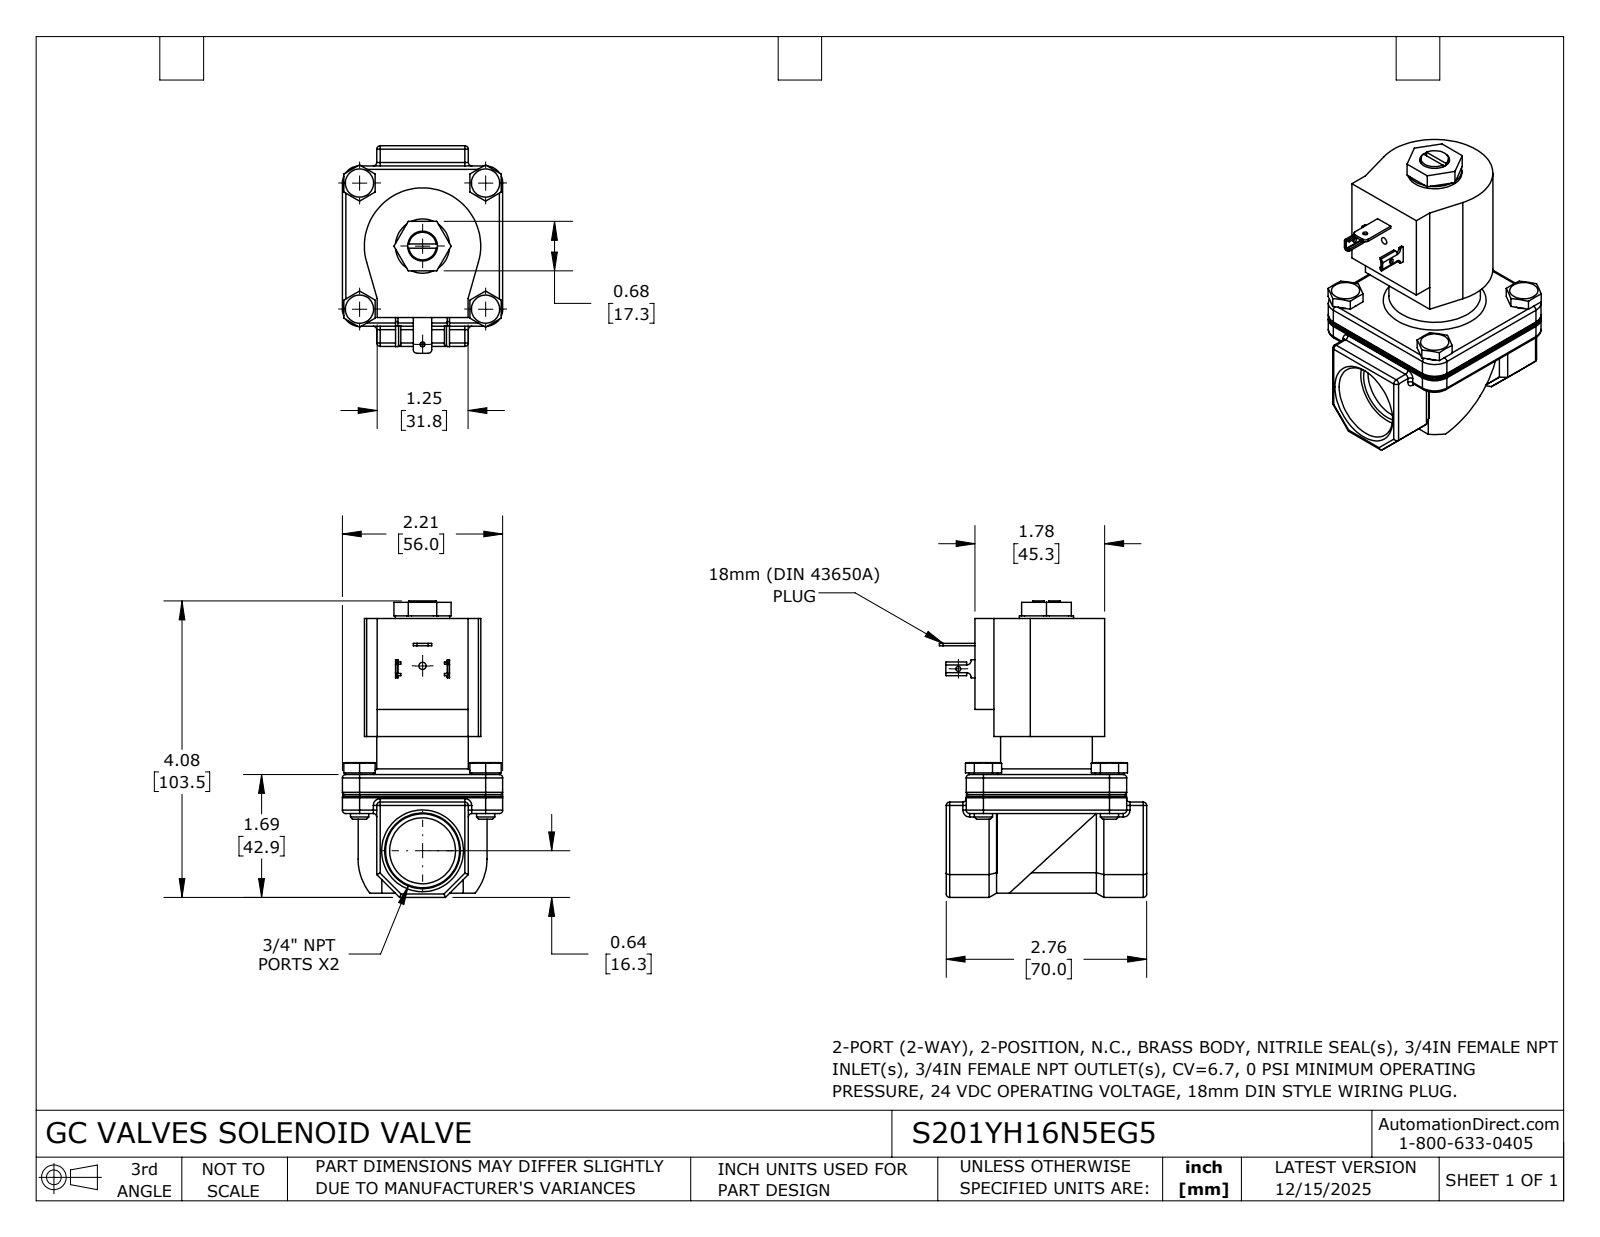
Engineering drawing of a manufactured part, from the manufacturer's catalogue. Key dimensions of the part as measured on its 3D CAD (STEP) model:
Part name (STEP PRODUCT): S201YH16N5EG5
STEP written by: SolidWorks 2024 (CONFIG_CONTROL_DESIGN)
Units: inches
Bodies: 1 solid, 338 faces (166 planar, 112 cylindrical, 60 other)
Overall size (bounding box): 4.075 × 2.851 × 2.205
Volume: 10.16 in³ · Surface area: 43.84 in²
Round holes (diameter × count): ⌀0.066 ×1, ⌀0.067 ×1, ⌀0.1 ×1, ⌀0.41 ×1, ⌀0.906 ×1
Round bosses / shafts (diameter × count): ⌀0.388 ×4, ⌀0.25 ×4, ⌀1.26 ×1, ⌀0.746 ×1, ⌀0.38 ×1
Partial cylindrical surfaces — rounded edges, fillets, slot ends (radius × count): R0.047 ×34, R0.006 ×4, R0.031 ×4, R0.041 ×4, R0.234 ×4, R0.236 ×4, R0.05 ×2, R0.06 ×2
Main face-to-face distances: 0.059, 2.143, 0.472, 1.732, 0.537, 2.68, 2.205, 1.094, 1.631, 3.774
Hole centre spacings: 1.35, 2.541
